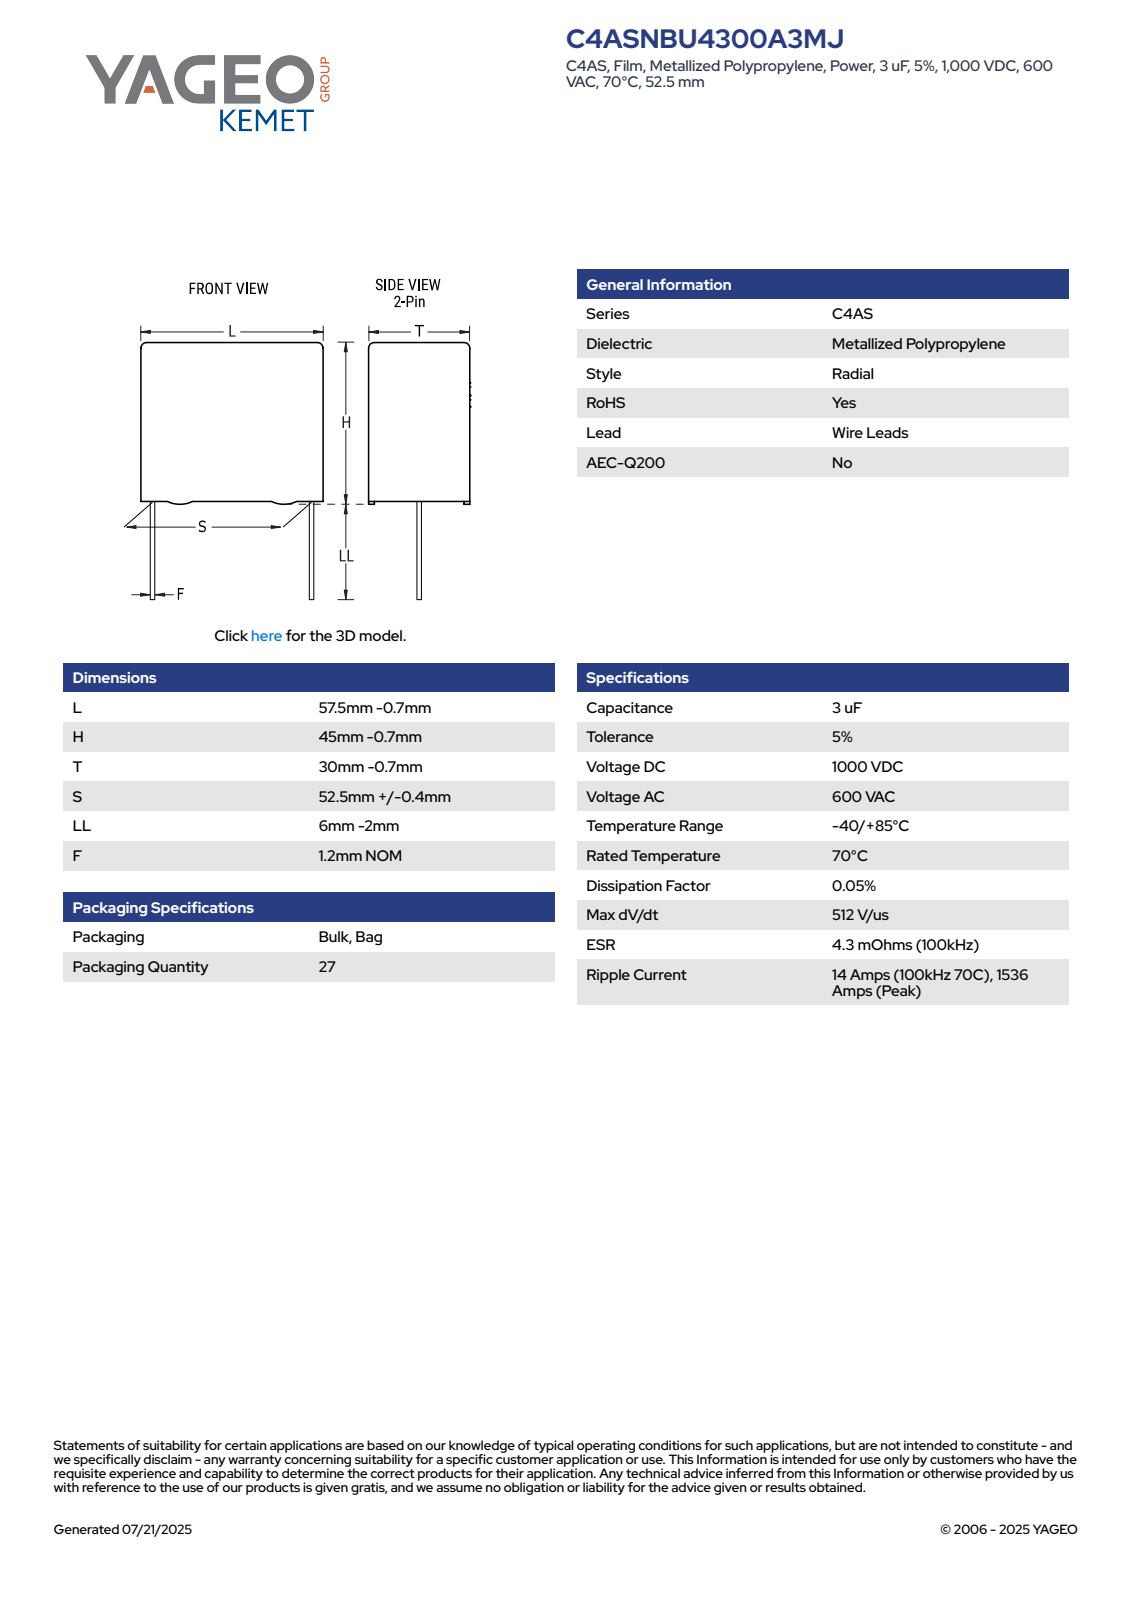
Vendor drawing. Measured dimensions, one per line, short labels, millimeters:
name: CFP_RB_57.5X45X30_L56.8H44.3T29.3S52.5LL4F1.2
written by: SolidWorks 2014 (AUTOMOTIVE_DESIGN)
unit: mm
bodies: 4 solids, 89 faces (81 planar, 8 cylindrical, 0 other)
size: 56.8 × 48.3 × 29.3
volume: 72 301 mm³; area: 11 019 mm²
bosses: 2× ⌀1.2
rounds: 4× R0.5
face distances: 29.3, 43.41, 56.8, 0.89, 44.3, 1.67, 27.63, 25.96, 40.77, 4
